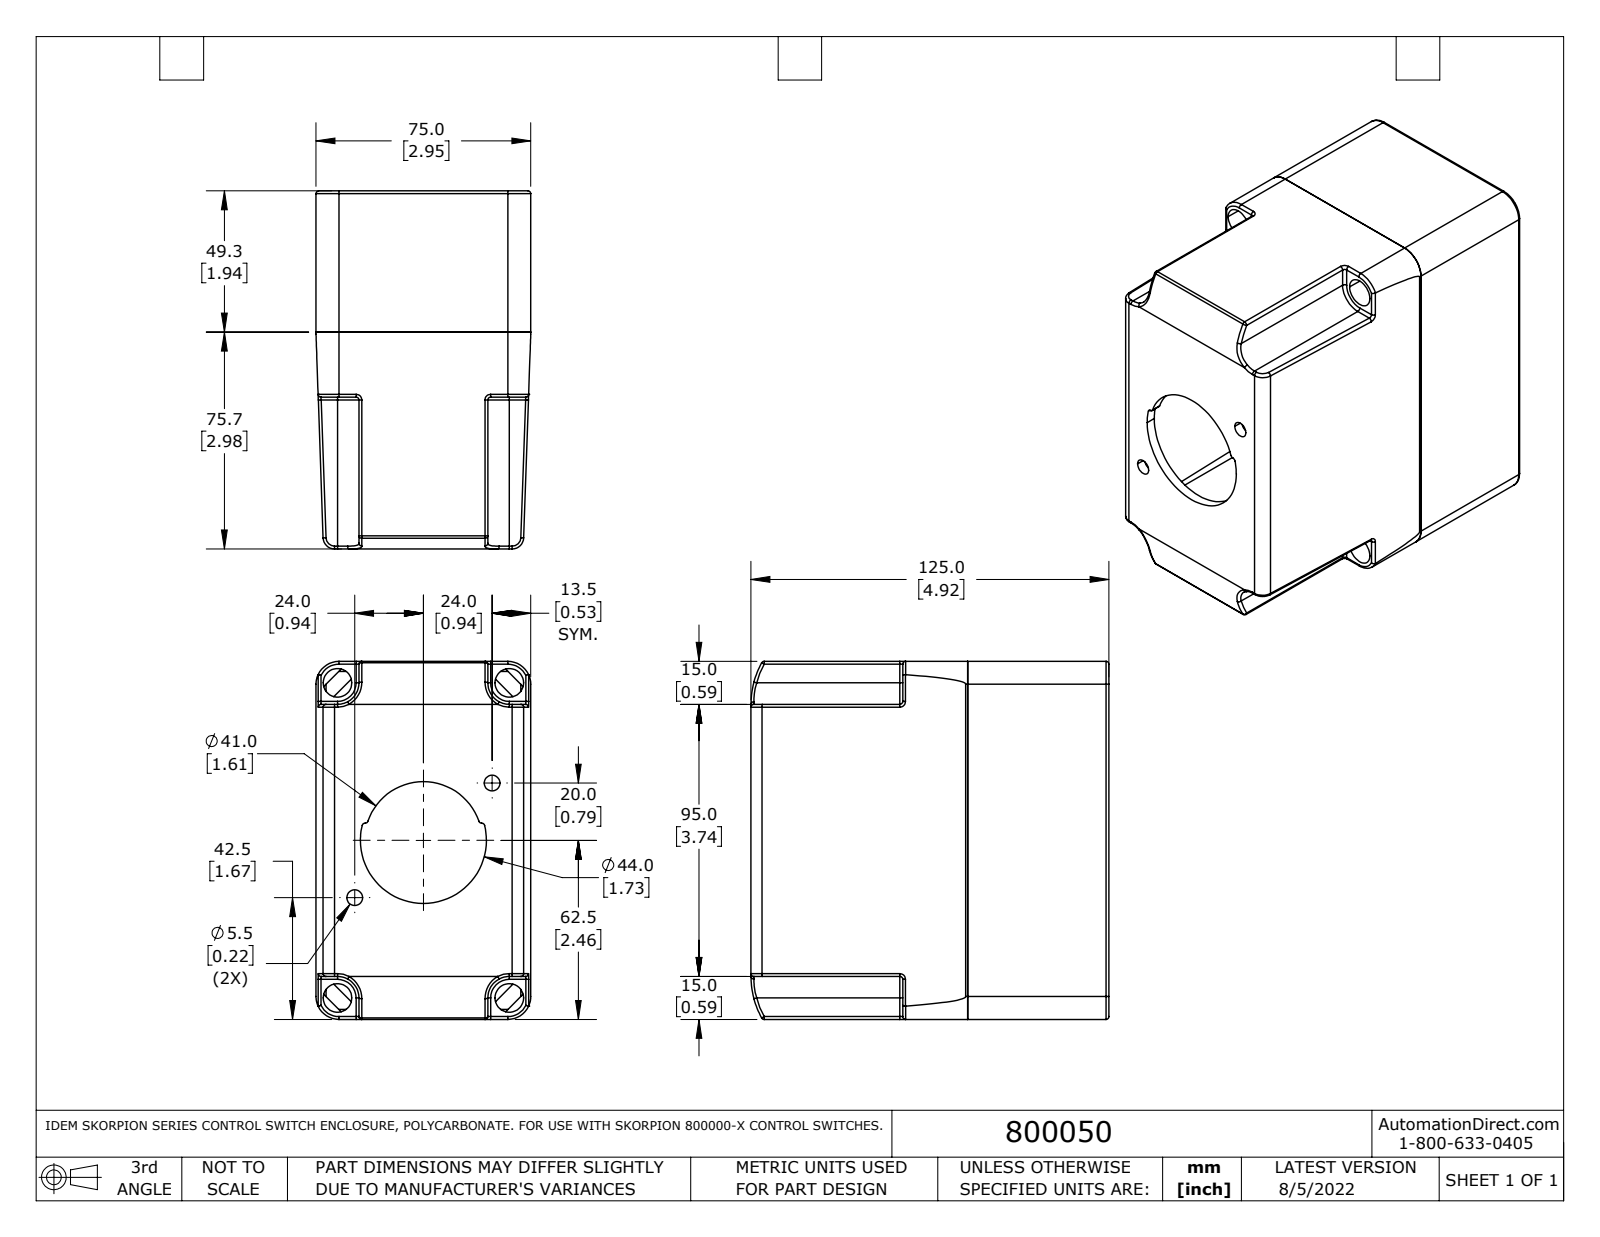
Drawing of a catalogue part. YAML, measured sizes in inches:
part_name: "800050"
step_written_by: "SolidWorks 2021 (AUTOMOTIVE_DESIGN)"
units: inches
bodies: {solids: 2, faces: 186, planar: 64, cylindrical: 82, other: 40}
overall_size: [4.921, 4.921, 2.953]
volume: 13.29
surface_area: 193.3
round_holes:
  - {diameter: 0.394, count: 4}
  - {diameter: 0.217, count: 2}
partial_cylinders:
  - {radius: 0.039, count: 28}
  - {radius: 0.177, count: 4}
  - {radius: 0.295, count: 4}
  - {radius: 0.315, count: 4}
  - {radius: 0.433, count: 4}
  - {radius: 0.02, count: 2}
  - {radius: 0.157, count: 2}
  - {radius: 1.043, count: 2}
face_to_face_distances: [0.138, 4.783, 4.921, 2.815, 4.646, 0.137, 2.953, 2.677, 0.591, 1.941]
hole_center_spacings: [1.398, 2.362, 2.533, 2.962, 3.639, 4.331, 4.933, 2.46]
